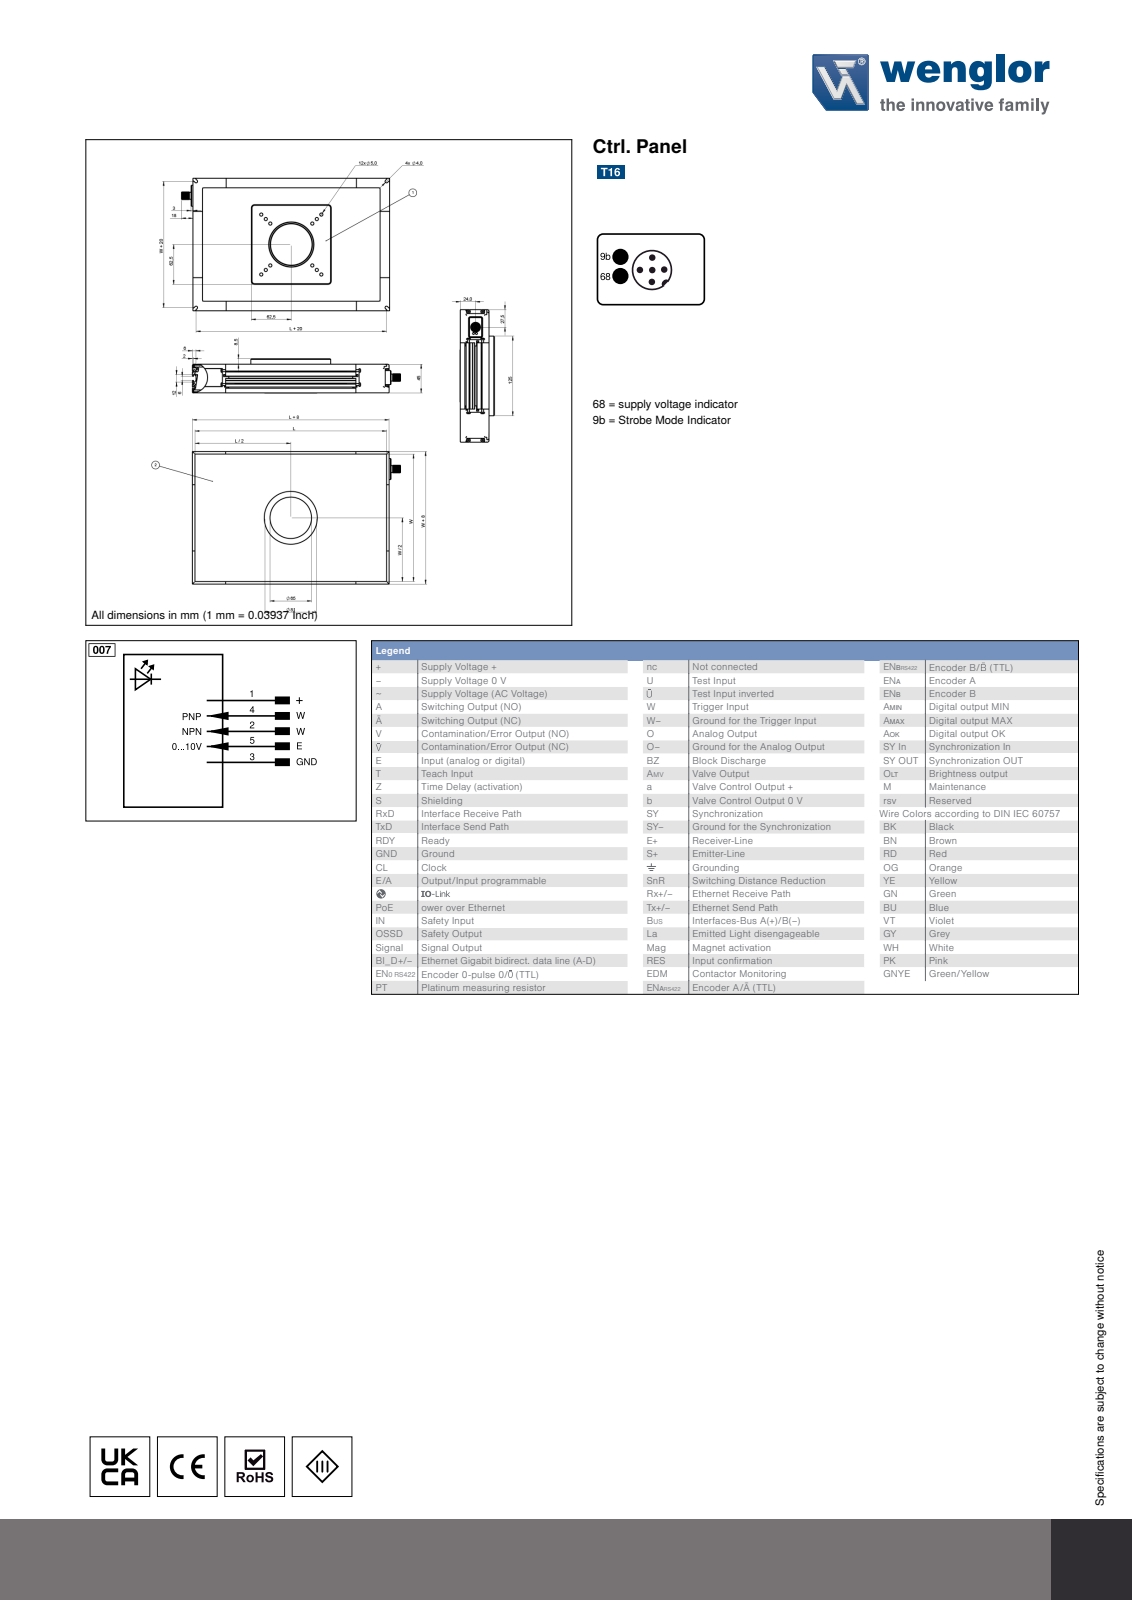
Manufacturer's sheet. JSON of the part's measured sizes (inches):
{"part_name": "OPT2435 and OPT2436", "step_written_by": "SolidWorks 2021 (AUTOMOTIVE_DESIGN)", "units": "inches", "bodies": {"solids": 1, "faces": 300, "planar": 155, "cylindrical": 129, "other": 16}, "overall_size": [8.894, 8.189, 2.12], "volume_in3": 105.6, "surface_area_in2": 236.8, "round_holes": [[0.197, 12], [0.118, 2], [0.327, 1], [2.559, 1]], "round_bosses_or_shafts": [[0.22, 8], [0.039, 5], [3.268, 1], [0.472, 1], [0.423, 1]], "partial_cylinders_radius": [[0.02, 20], [0.197, 8], [0.089, 4], [0.118, 4], [0.024, 1]], "face_to_face_distances": [1.648, 0.394, 2.041, 8.189, 0.24, 7.949, 0.079, 1.726, 0.315, 1.634], "hole_center_spacings": [0.394, 2.881, 3.194, 3.435, 4.449, 0.787, 1.831, 2.224]}
